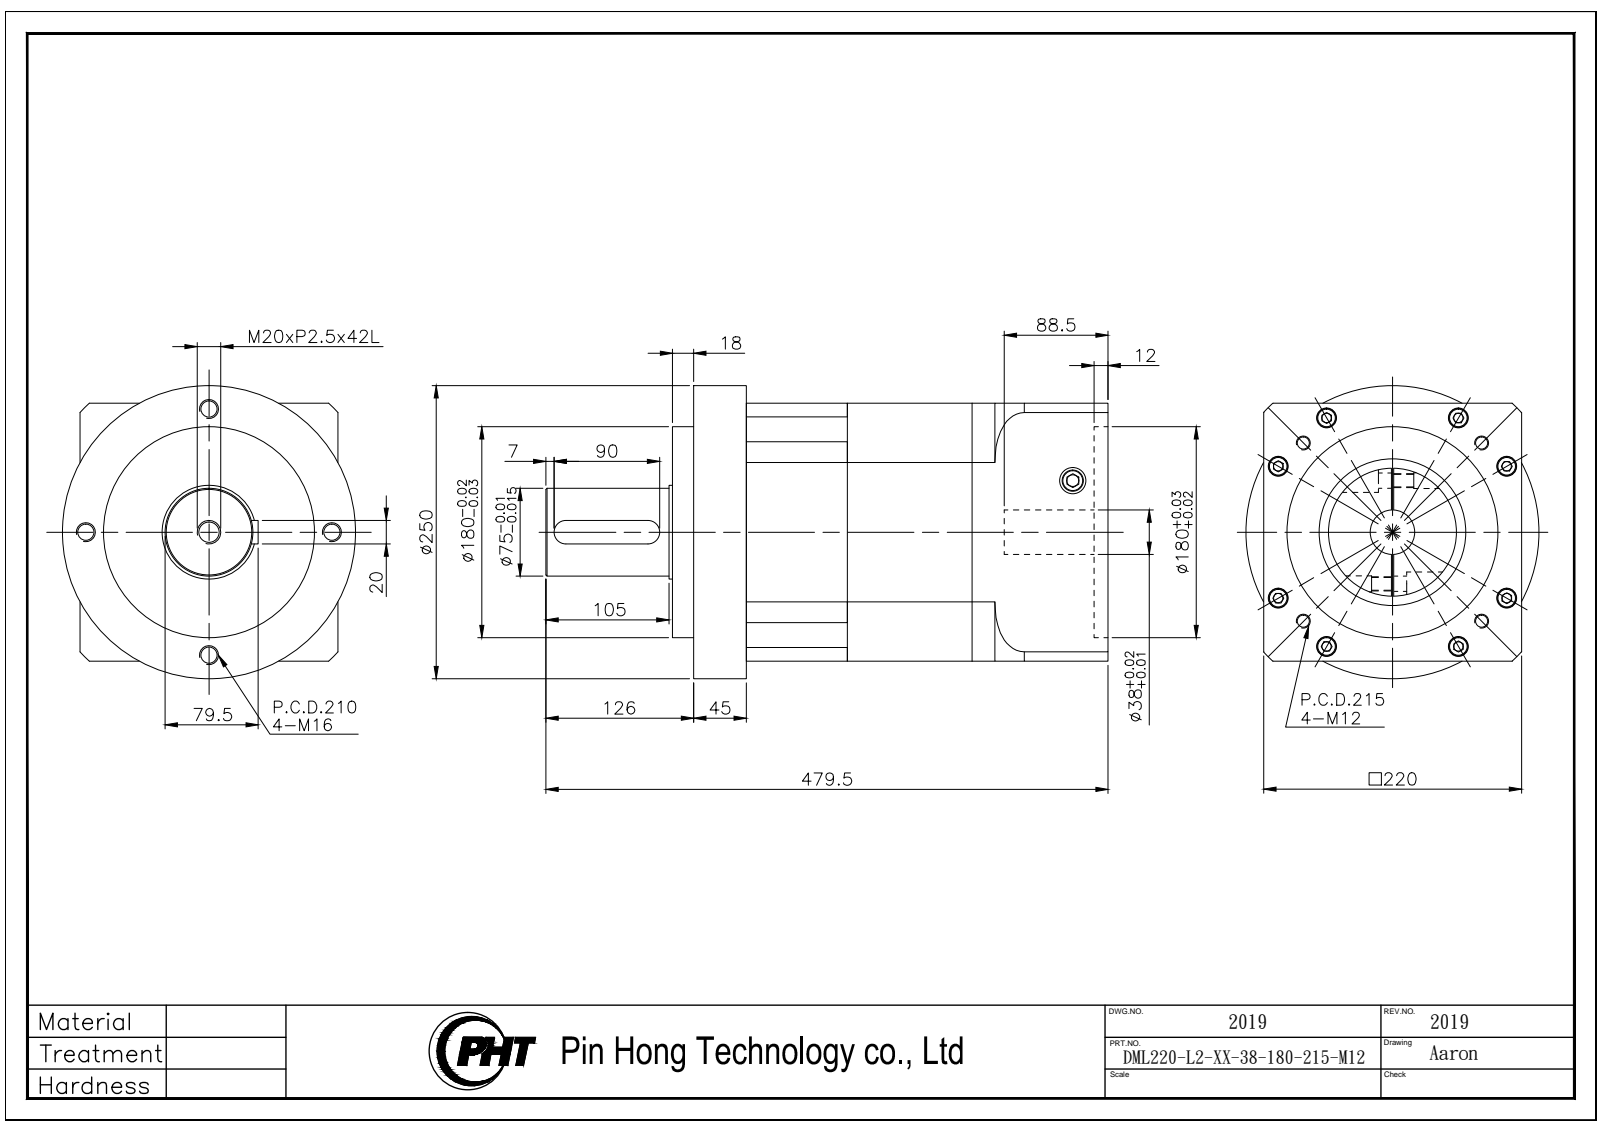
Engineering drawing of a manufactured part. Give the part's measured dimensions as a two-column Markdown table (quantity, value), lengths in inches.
| quantity | value |
| --- | --- |
| part name | DML220-L2-XX-38-180-215-M12_2019 |
| STEP written by | SolidWorks 2016 (AUTOMOTIVE_DESIGN) |
| units | inches |
| bodies | 4 solids, 271 faces (114 planar, 117 cylindrical, 40 other) |
| overall size | 18.878 × 9.843 × 9.843 |
| volume | 988.6 in³ |
| surface area | 1 297 in² |
| round holes (diameter × count) | 0.433 × 8, 0.669 × 8, 0.402 × 4, 0.551 × 4, 0.886 × 2, 0.689 × 1, 1.496 × 1, 4.921 × 1, 7.087 × 1 |
| round bosses / shafts (diameter × count) | 0.63 × 8, 9.843 × 1, 4.291 × 1, 3.15 × 1, 2.953 × 1 |
| partial cylindrical surfaces (radius × count) | 0.591 × 4, 0.394 × 2, 5.906 × 1 |
| main face-to-face distances | 8.661, 7.579, 4.193, 3.386, 9.35, 5.157, 1.772, 4.567, 8.76, 12.146 |
| hole center spacings | 4.429, 1.147, 2.235, 3.203, 4.289, 5.275, 6.264, 6.872 |
